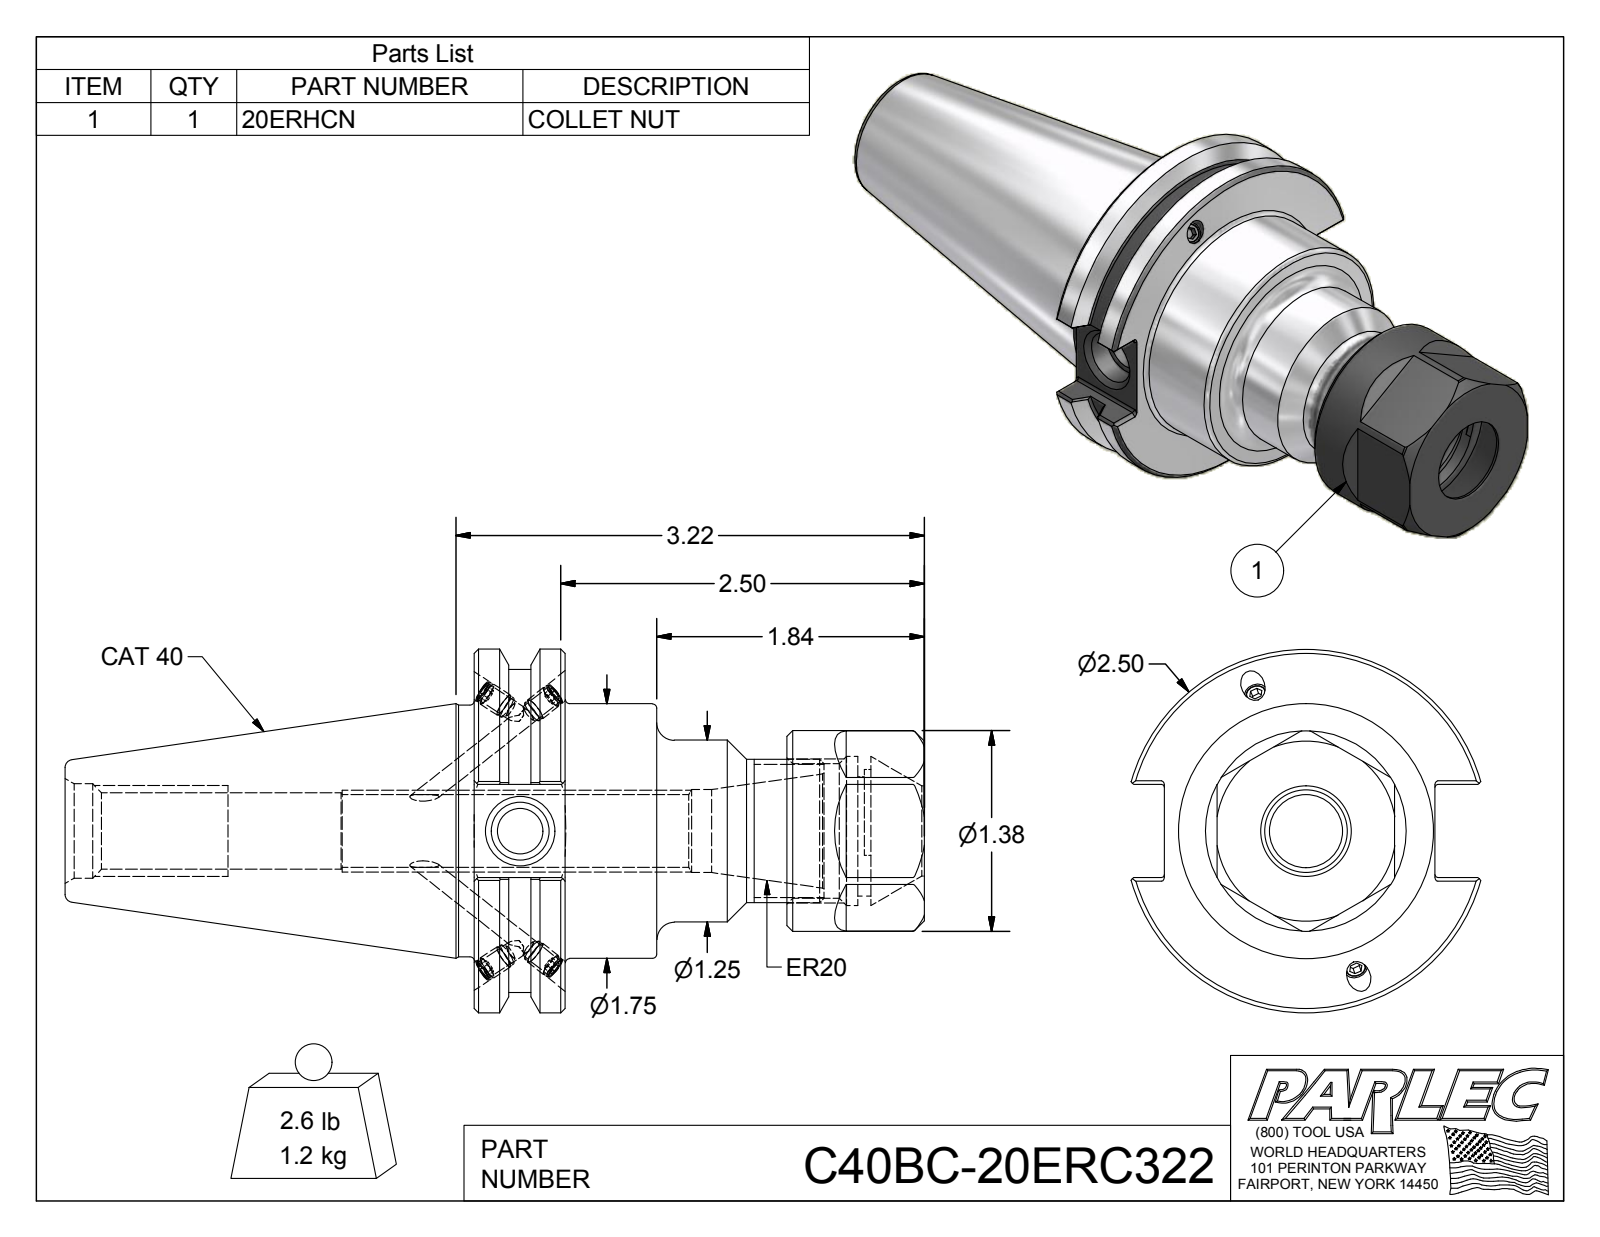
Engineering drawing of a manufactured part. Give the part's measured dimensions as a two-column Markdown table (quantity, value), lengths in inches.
| quantity | value |
| --- | --- |
| part name | C40BC-20ERC322; C40BCB-20ER3-1; 029-965; 20ERHCN |
| STEP written by | Autodesk Inventor 2012 (AUTOMOTIVE_DESIGN) |
| units | inches |
| bodies | 6 solids, 212 faces (93 planar, 54 cylindrical, 65 other) |
| overall size | 5.907 × 2.5 × 2.406 |
| volume | 8.991 in³ |
| surface area | 51.99 in² |
| round holes (diameter × count) | 0.13 × 4, 0.161 × 4, 0.315 × 1, 0.399 × 1, 0.502 × 1, 0.527 × 1, 0.57 × 1, 0.62 × 1, 0.648 × 1, 0.82 × 1, 0.925 × 1, 1.024 × 1 |
| round bosses / shafts (diameter × count) | 0.165 × 4, 0.157 × 4, 2.5 × 1, 2.219 × 1, 1.75 × 1, 1.73 × 1, 1.378 × 1, 1.25 × 1 |
| partial cylindrical surfaces (radius × count) | 0.02 × 12, 0.423 × 1 |
| main face-to-face distances | 0.625, 1.22, 3.095, 2.47, 2.15, 1.525, 0.945, 1.255, 0.63, 0.895 |
| hole center spacings | 0.037 |
